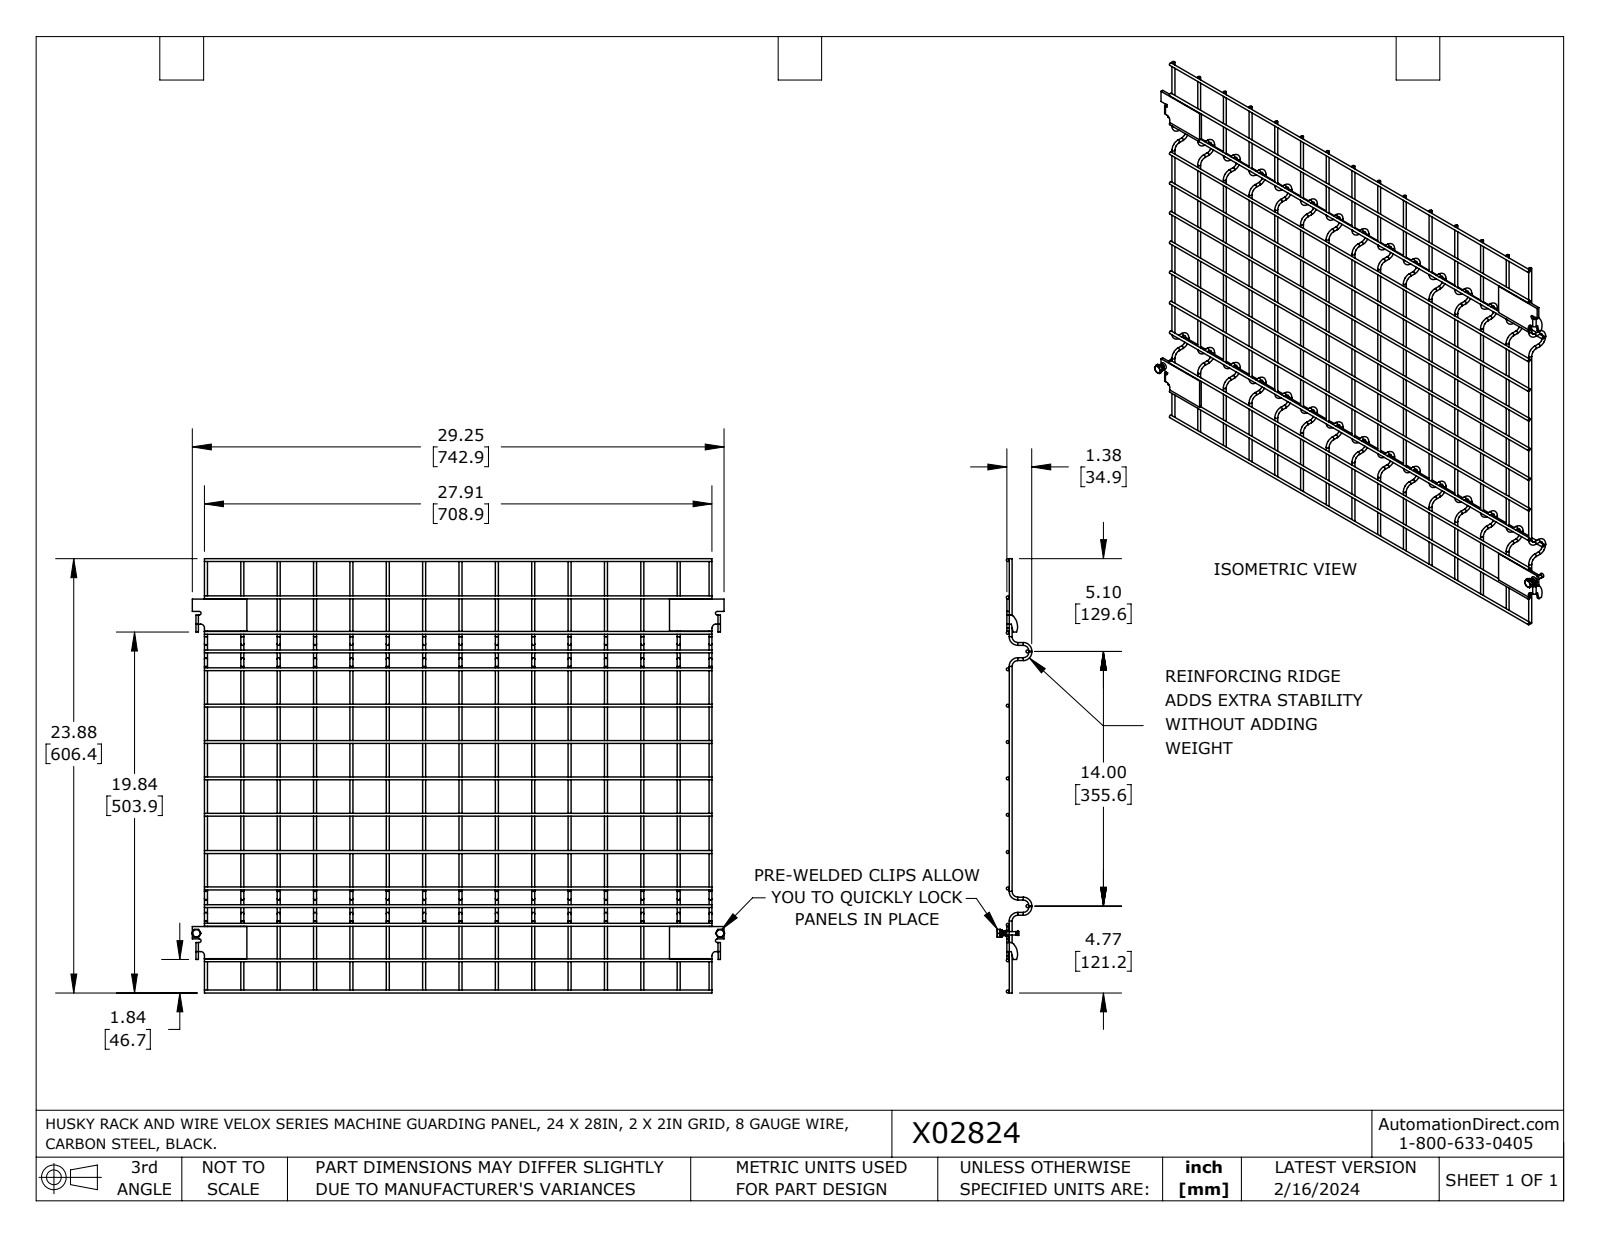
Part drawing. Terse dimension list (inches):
name: X02824
written by: SolidWorks 2023 (AUTOMOTIVE_DESIGN)
unit: in
bodies: 38 solids, 470 faces (140 planar, 186 cylindrical, 144 other)
size: 29.313 × 23.875 × 1.853
volume: 19.29 in³; area: 464.3 in²
holes: 2× ⌀0.201, 2× ⌀0.25
bosses: 105× ⌀0.16, 2× ⌀0.39, 2× ⌀0.245, 2× ⌀0.187
rounds: 4× R0.1, 4× R0.218, 2× R0.009, 2× R0.067, 2× R0.134, 2× R0.25, 2× R0.865
face distances: 0.134, 0.125, 2.798, 26.046, 18, 18, 0.467, 28.377, 2.331, 25.579
hole spacings: 28.808
